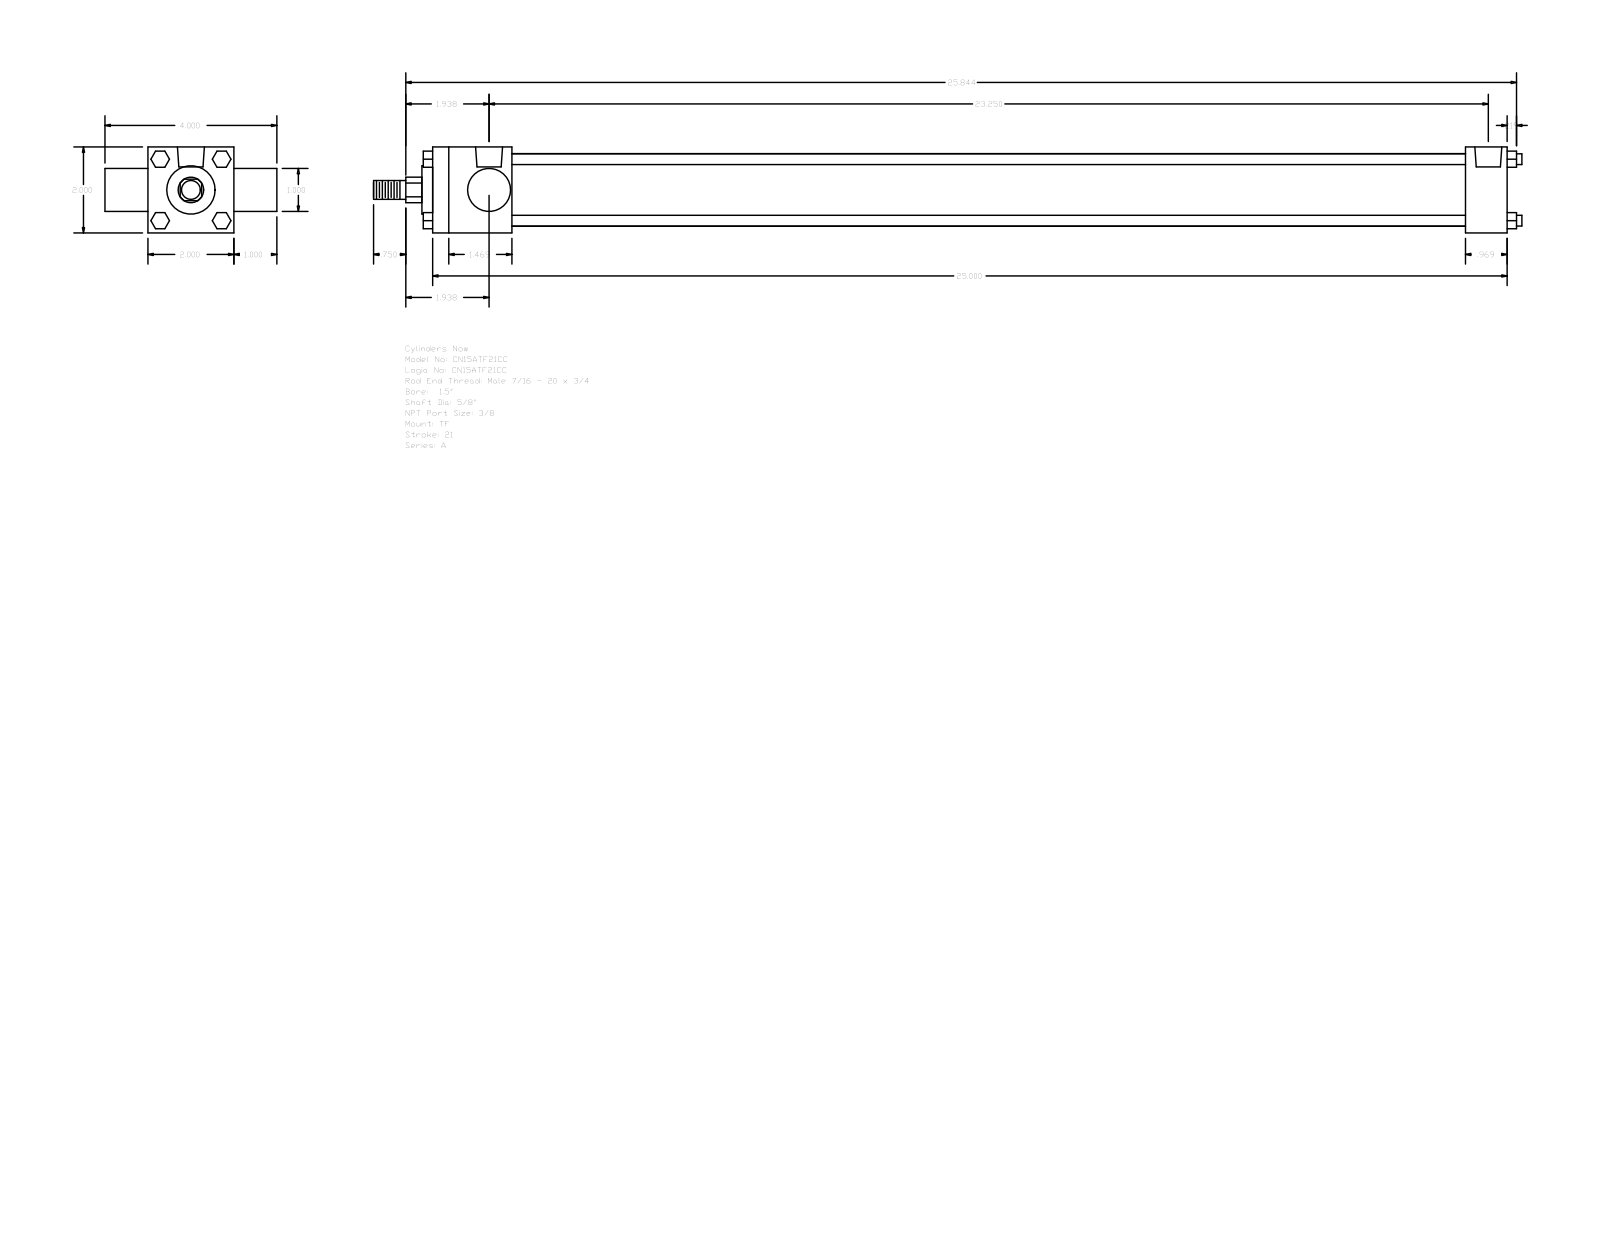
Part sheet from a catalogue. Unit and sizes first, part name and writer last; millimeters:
Units: millimetres
Overall size (bounding box): 678.66 × 101.6 × 50.8
Round holes (diameter × count): ⌀5.56 ×3, ⌀15.93 ×2
Round bosses / shafts (diameter × count): ⌀6.35 ×4, ⌀42.93 ×1, ⌀28.57 ×1, ⌀25.4 ×1, ⌀15.88 ×1, ⌀11.11 ×1
Partial cylindrical surfaces — rounded edges, fillets, slot ends (radius × count): R7.54 ×1
Main face-to-face distances: 50.8, 635, 25.4, 76.2, 46.83, 610.39, 563.56, 588.17, 24.61, 101.6
Hole centre spacings: 3.97, 586.58, 582.61, 590.55
Bodies: 0 solids, 120 faces (92 planar, 28 cylindrical, 0 other)
Part name (STEP PRODUCT): A_TF__0150_0.625
STEP written by: GSSL Pune (CONFIG_CONTROL_DESIGN)
